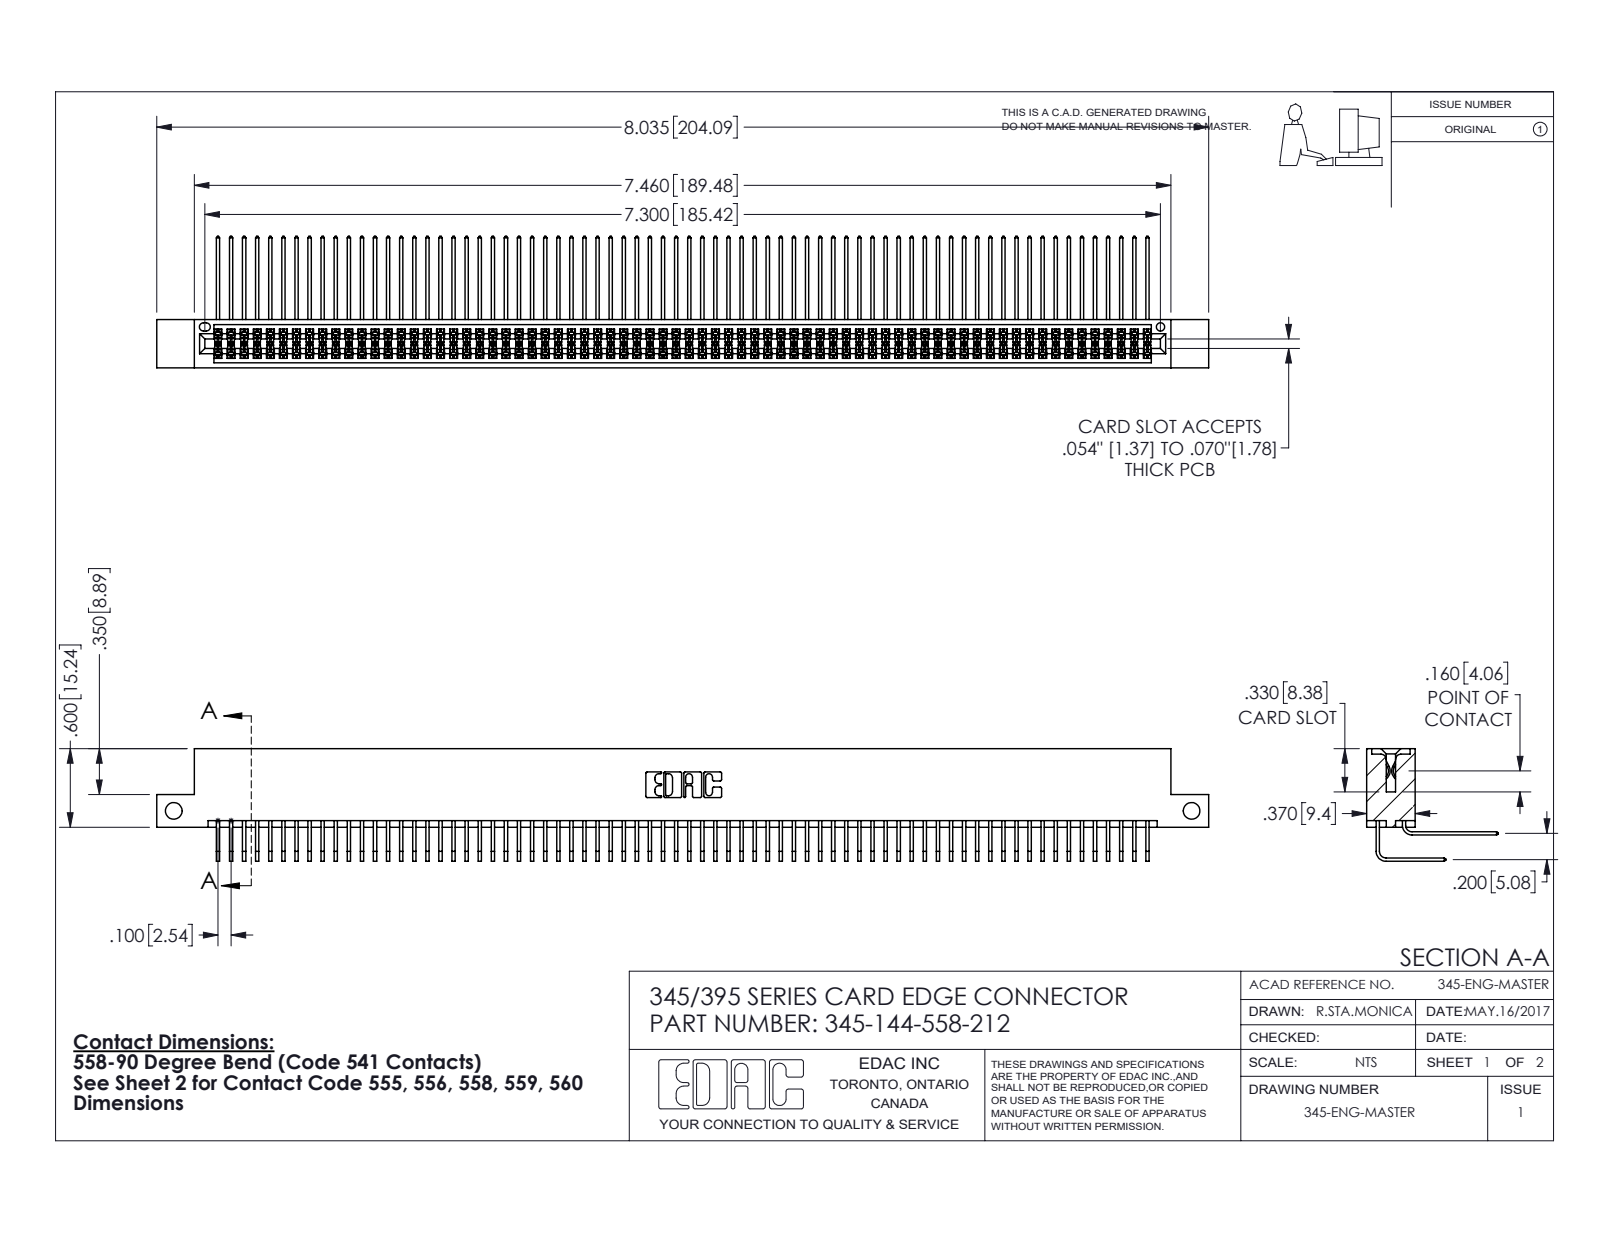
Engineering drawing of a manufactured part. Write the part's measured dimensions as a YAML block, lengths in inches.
part_name: "345-292-001_558 559 Tail - 1; 345-144-558-212; 345 Part_Flush Mounting Lugs - Side Mount; 345-292-001_558 Tail - 2"
step_written_by: "SolidWorks 2016 (CONFIG_CONTROL_DESIGN)"
units: inches
bodies: {solids: 145, faces: 7614, planar: 5120, cylindrical: 2494, other: 0}
overall_size: [8.035, 1.005, 0.859]
volume: 1.272
surface_area: 54.51
round_holes:
  - {diameter: 0.128, count: 2}
  - {diameter: 0.064, count: 1}
partial_cylinders:
  - {radius: 0.006, count: 288}
  - {radius: 0.01, count: 22}
  - {radius: 0.007, count: 6}
  - {radius: 0.031, count: 6}
  - {radius: 0.026, count: 3}
  - {radius: 0.014, count: 2}
  - {radius: 0.019, count: 2}
  - {radius: 0.022, count: 2}
face_to_face_distances: [0.072, 0.298, 0.2, 0.37, 0.098, 0.272, 0.025, 0.225, 0.025, 0.175]
hole_center_spacings: [7.775]
